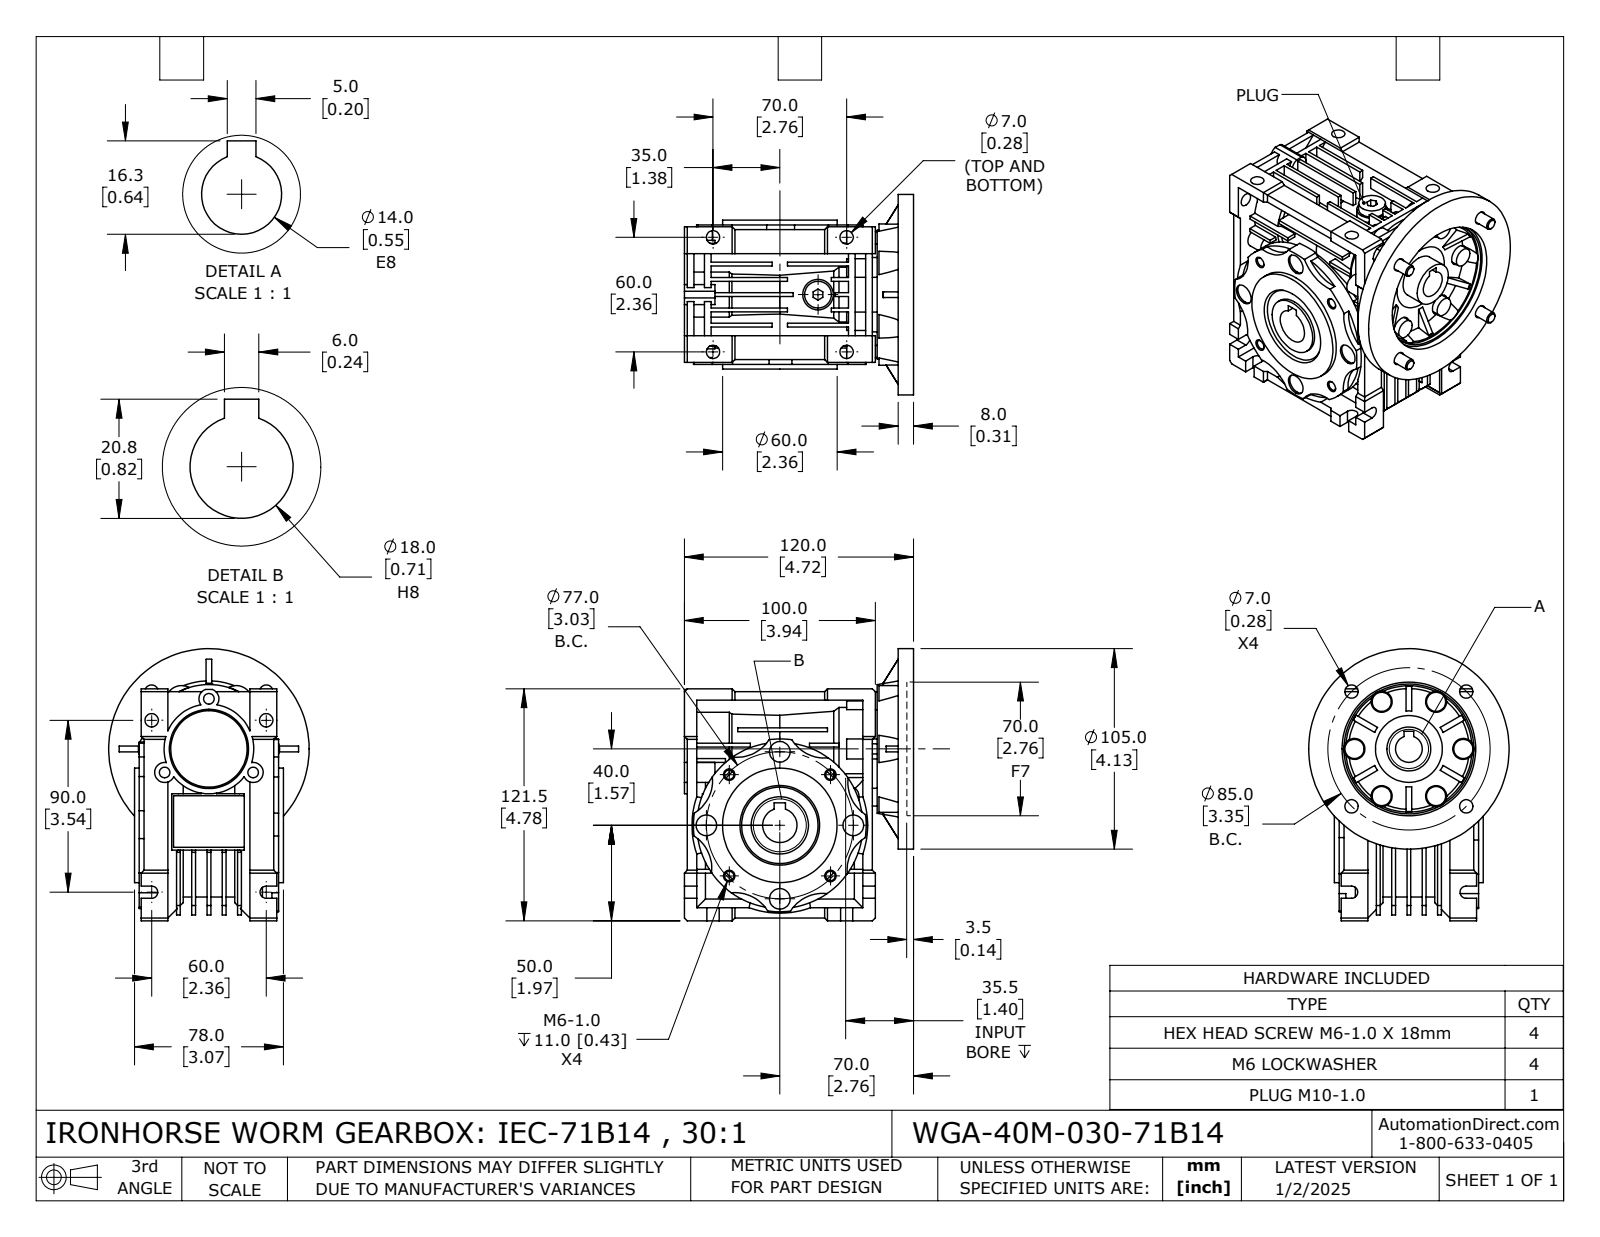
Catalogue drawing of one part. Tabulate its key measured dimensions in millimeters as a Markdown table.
| quantity | value |
| --- | --- |
| part name | WGA-40M-030-71B14 |
| STEP written by | SolidWorks 2024 (CONFIG_CONTROL_DESIGN) |
| units | millimeters |
| bodies | 14 solids, 956 faces (550 planar, 281 cylindrical, 125 other) |
| overall size | 142.5 × 128.5 × 105 |
| volume | 688 964 mm³ |
| surface area | 170 588 mm² |
| round holes (diameter × count) | 7 × 10, 11 × 6, 4.92 × 4, 6.1 × 4, 10.8 × 4, 5.55 × 3, 9 × 1, 14 × 1, 15 × 1, 18 × 1, 23 × 1, 28 × 1 |
| round bosses / shafts (diameter × count) | 10 × 6, 12.2 × 4, 6 × 4, 105 × 1, 75 × 1, 60 × 1, 54 × 1, 47 × 1 |
| partial cylindrical surfaces (radius × count) | 20 × 8, 3.2 × 6, 5.22 × 6, 8.5 × 6, 5.25 × 3, 34.31 × 1, 43.5 × 1, 43.59 × 1 |
| main face-to-face distances | 8, 6, 2, 1.5, 16, 10, 5, 11, 2.5, 24 |
| hole center spacings | 28.5, 29.1, 70.22, 49.36, 16.69, 30.09, 33.54, 37.5 |
